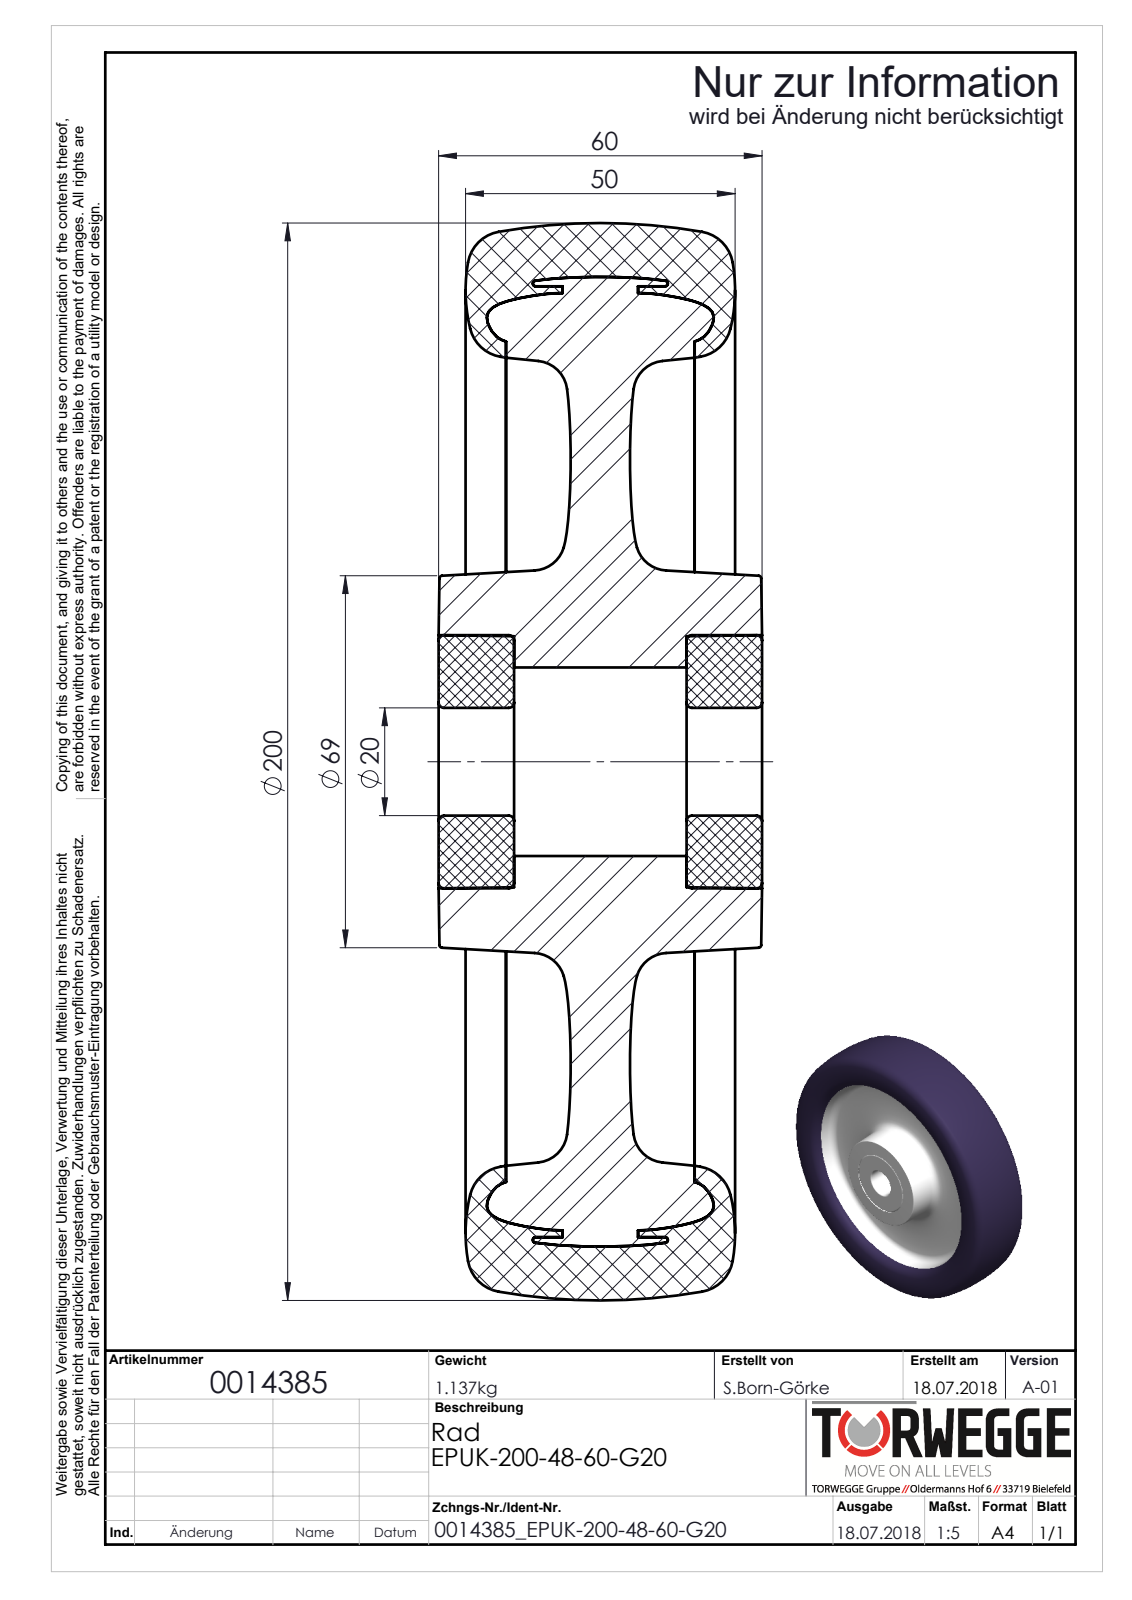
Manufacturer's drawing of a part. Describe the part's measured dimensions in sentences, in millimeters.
The part is named "0014385_EPUK-200-48-60-G20". Its 3-D file was written by "SolidWorks 2016 (AUTOMOTIVE_DESIGN)". It is 0 solids with 72 faces: 4 planar, 6 cylindrical and 62 other. Overall it measures 200 by 198.37 by 60 millimeters. Round holes: 1 of diameter 20, 1 of diameter 35. The main face-to-face distances are 12.5, 47.5, 35, 60.
